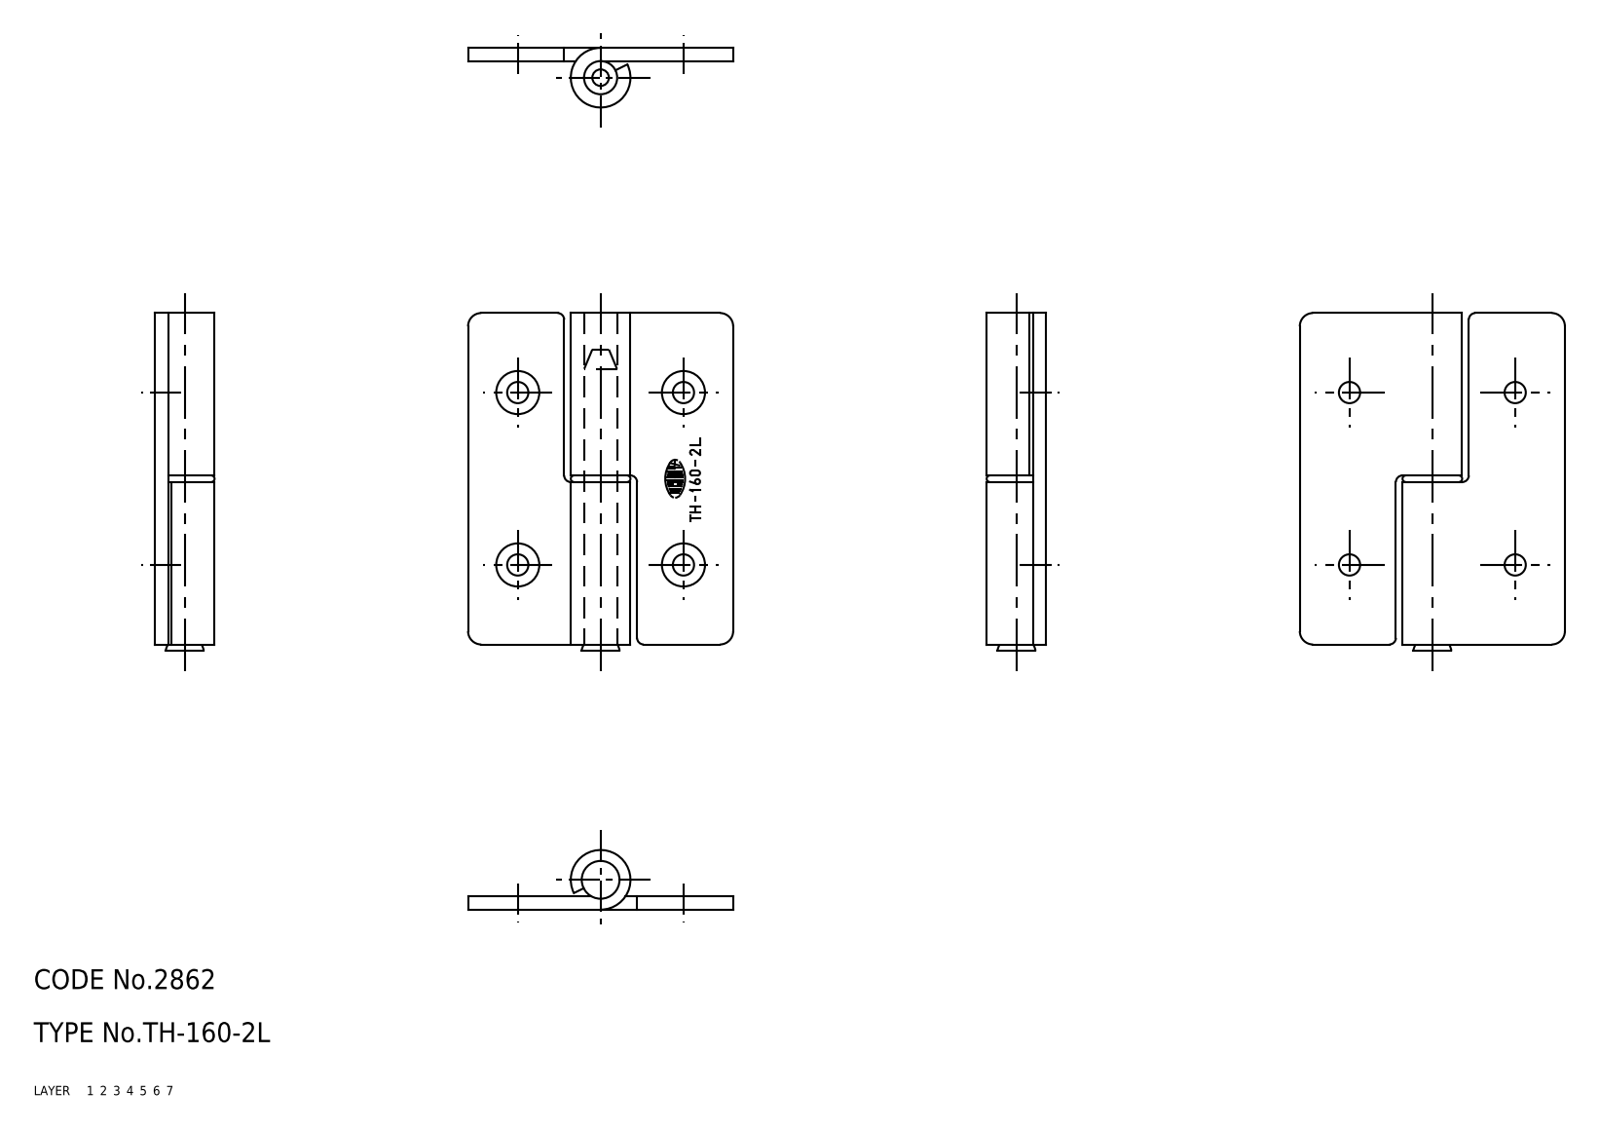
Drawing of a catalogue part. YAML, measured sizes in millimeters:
part_name: "67112661; 67112674; 67112687"
step_written_by: "CADfix (AUTOMOTIVE_DESIGN)"
units: millimeters
bodies: {solids: 3, faces: 60, planar: 0, cylindrical: 0, other: 60}
overall_size: [51, 40, 9]
volume: 5984
surface_area: 6721
